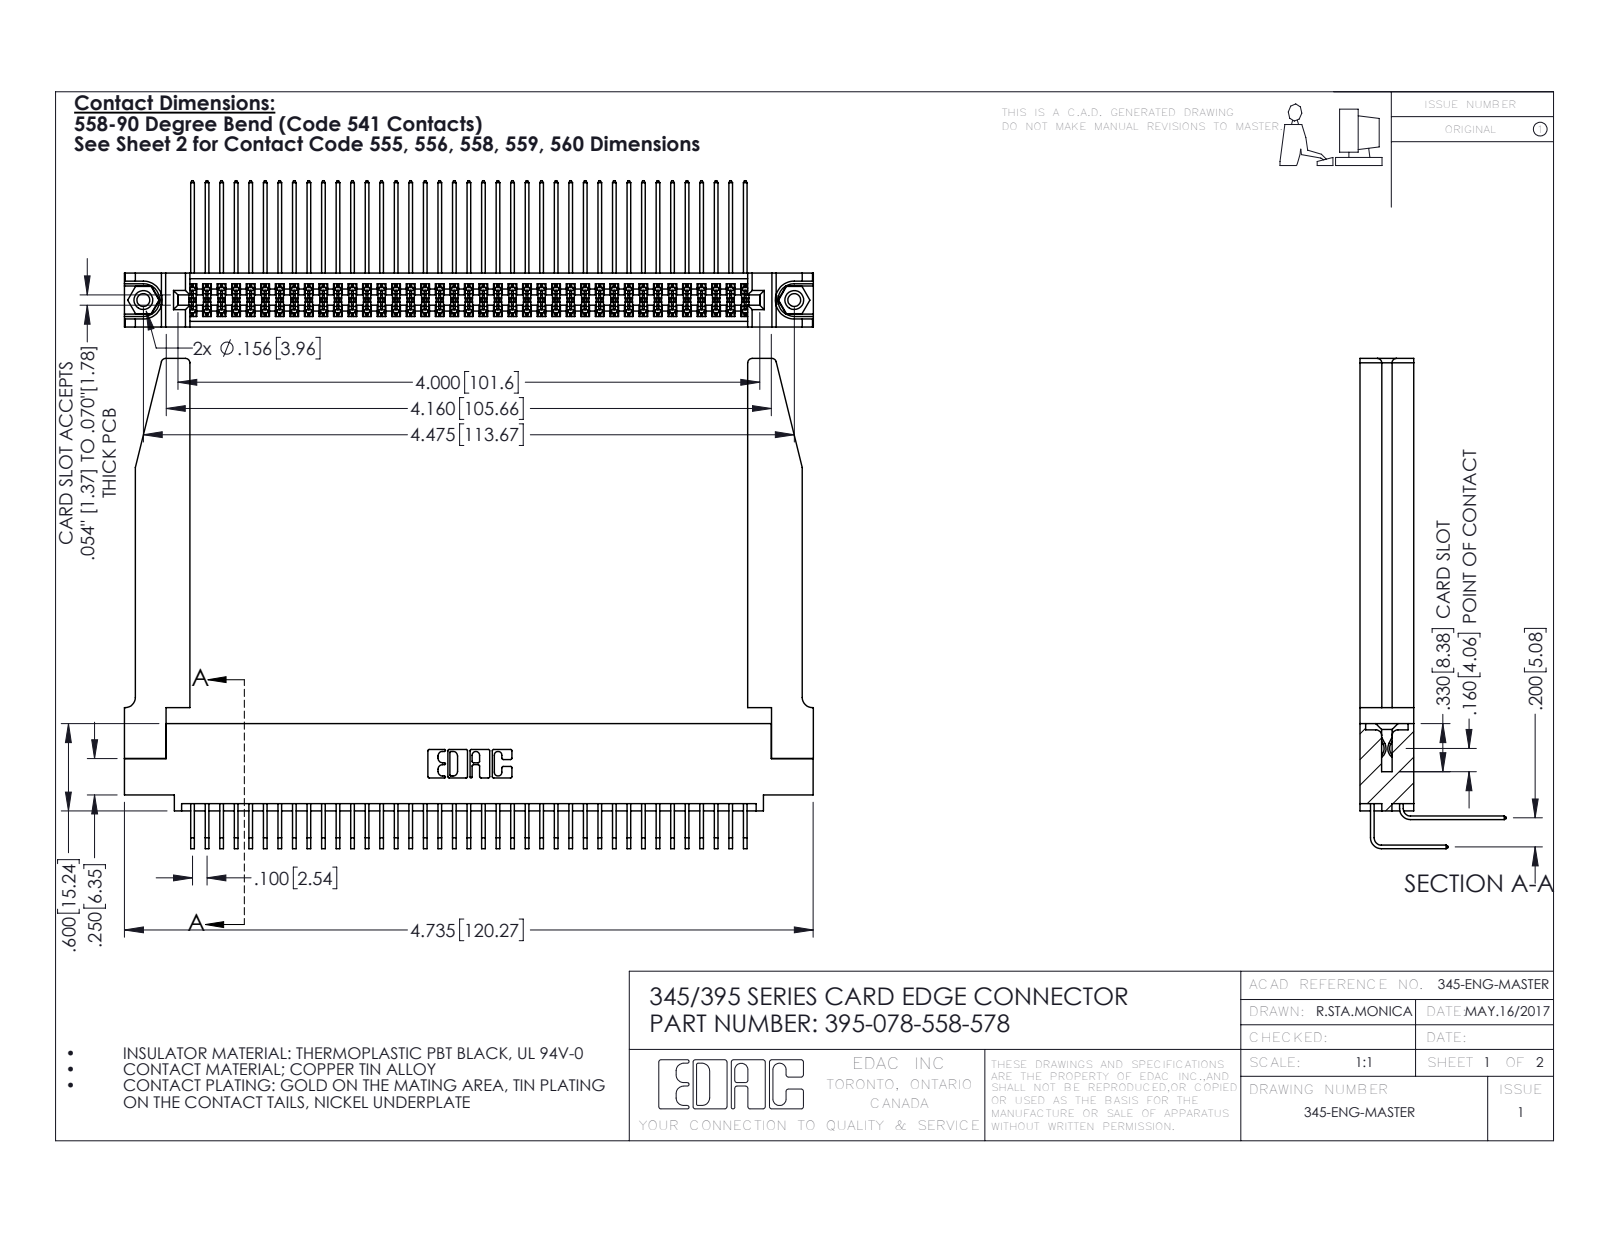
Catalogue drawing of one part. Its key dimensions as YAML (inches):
part_name: "345-220-078_345-220-078; 345-292-001_558 Tail - 2; 345-250-001_345-250-001-102; 345-292-001_558 559 Tail - 1 (+2 more)"
step_written_by: "SolidWorks 2016 (CONFIG_CONTROL_DESIGN)"
units: inches
bodies: {solids: 83, faces: 4420, planar: 2956, cylindrical: 1412, other: 52}
overall_size: [4.736, 3.369, 1.005]
volume: 1.209
surface_area: 41.51
round_holes:
  - {diameter: 0.089, count: 2}
  - {diameter: 0.125, count: 2}
  - {diameter: 0.156, count: 2}
  - {diameter: 0.064, count: 1}
round_bosses_or_shafts:
  - {diameter: 0.155, count: 2}
partial_cylinders:
  - {radius: 0.006, count: 118}
  - {radius: 0.01, count: 22}
  - {radius: 0.03, count: 8}
  - {radius: 0.007, count: 6}
  - {radius: 0.031, count: 6}
  - {radius: 0.026, count: 3}
  - {radius: 0.014, count: 2}
  - {radius: 0.019, count: 2}
face_to_face_distances: [0.37, 0.072, 0.298, 0.2, 0.098, 0.272, 0.025, 0.225, 0.148, 0.15]
hole_center_spacings: [0.27, 4.239, 4.475]
